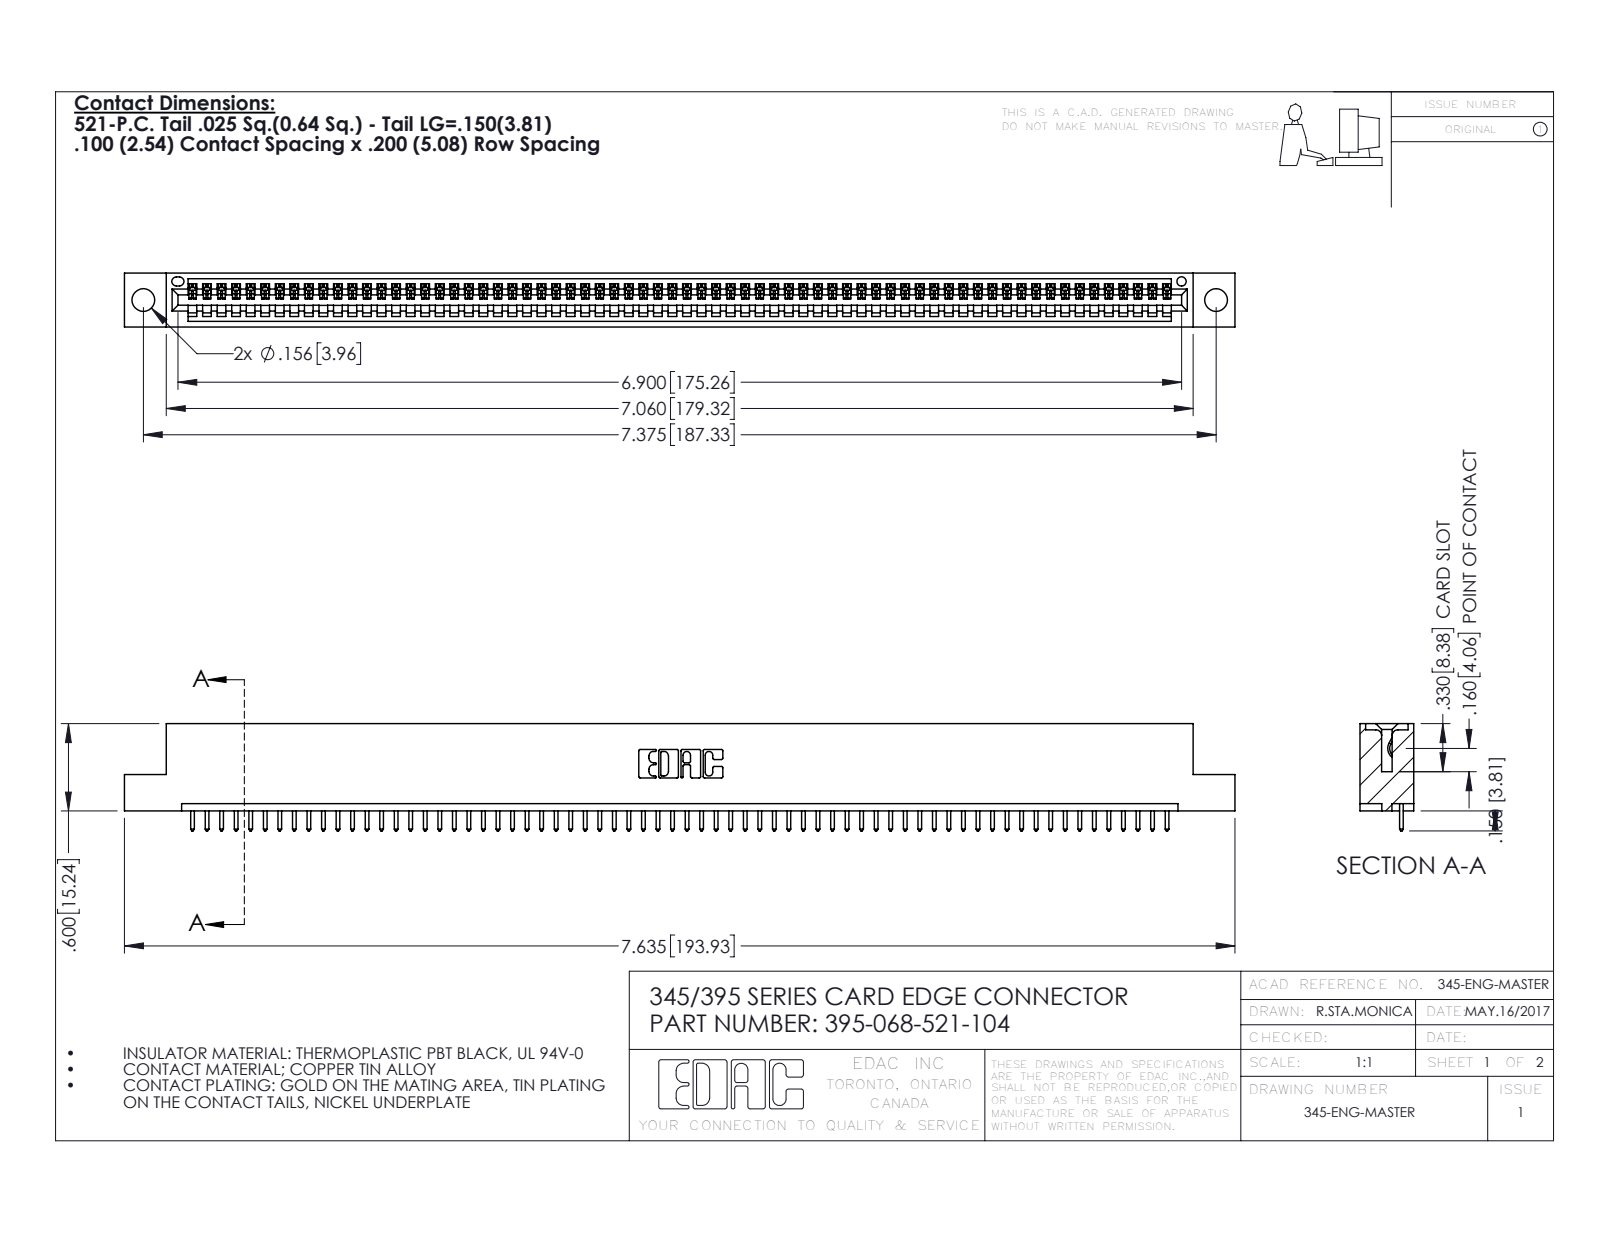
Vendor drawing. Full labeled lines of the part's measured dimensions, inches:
Part name (STEP PRODUCT): 345 Part_Flush Mounting Lugs - 0.156 Dia-TH; 395-068-521-104; 345-292-001_345-293-121
STEP written by: SolidWorks 2016 (CONFIG_CONTROL_DESIGN)
Units: inches
Bodies: 69 solids, 4070 faces (2800 planar, 1270 cylindrical, 0 other)
Overall size (bounding box): 7.635 × 0.737 × 0.37
Volume: 1.12 in³ · Surface area: 36.88 in²
Round holes (diameter × count): ⌀0.156 ×2, ⌀0.064 ×1
Partial cylindrical surfaces — rounded edges, fillets, slot ends (radius × count): R0.006 ×136, R0.01 ×136, R0.01 ×22, R0.007 ×6, R0.031 ×6, R0.026 ×3, R0.031 ×2, R0.04 ×2
Main face-to-face distances: 0.298, 0.072, 0.37, 0.2, 0.098, 0.272, 0.025, 0.225, 0.149, 0.072
Hole centre spacings: 0.27, 7.139, 7.375
